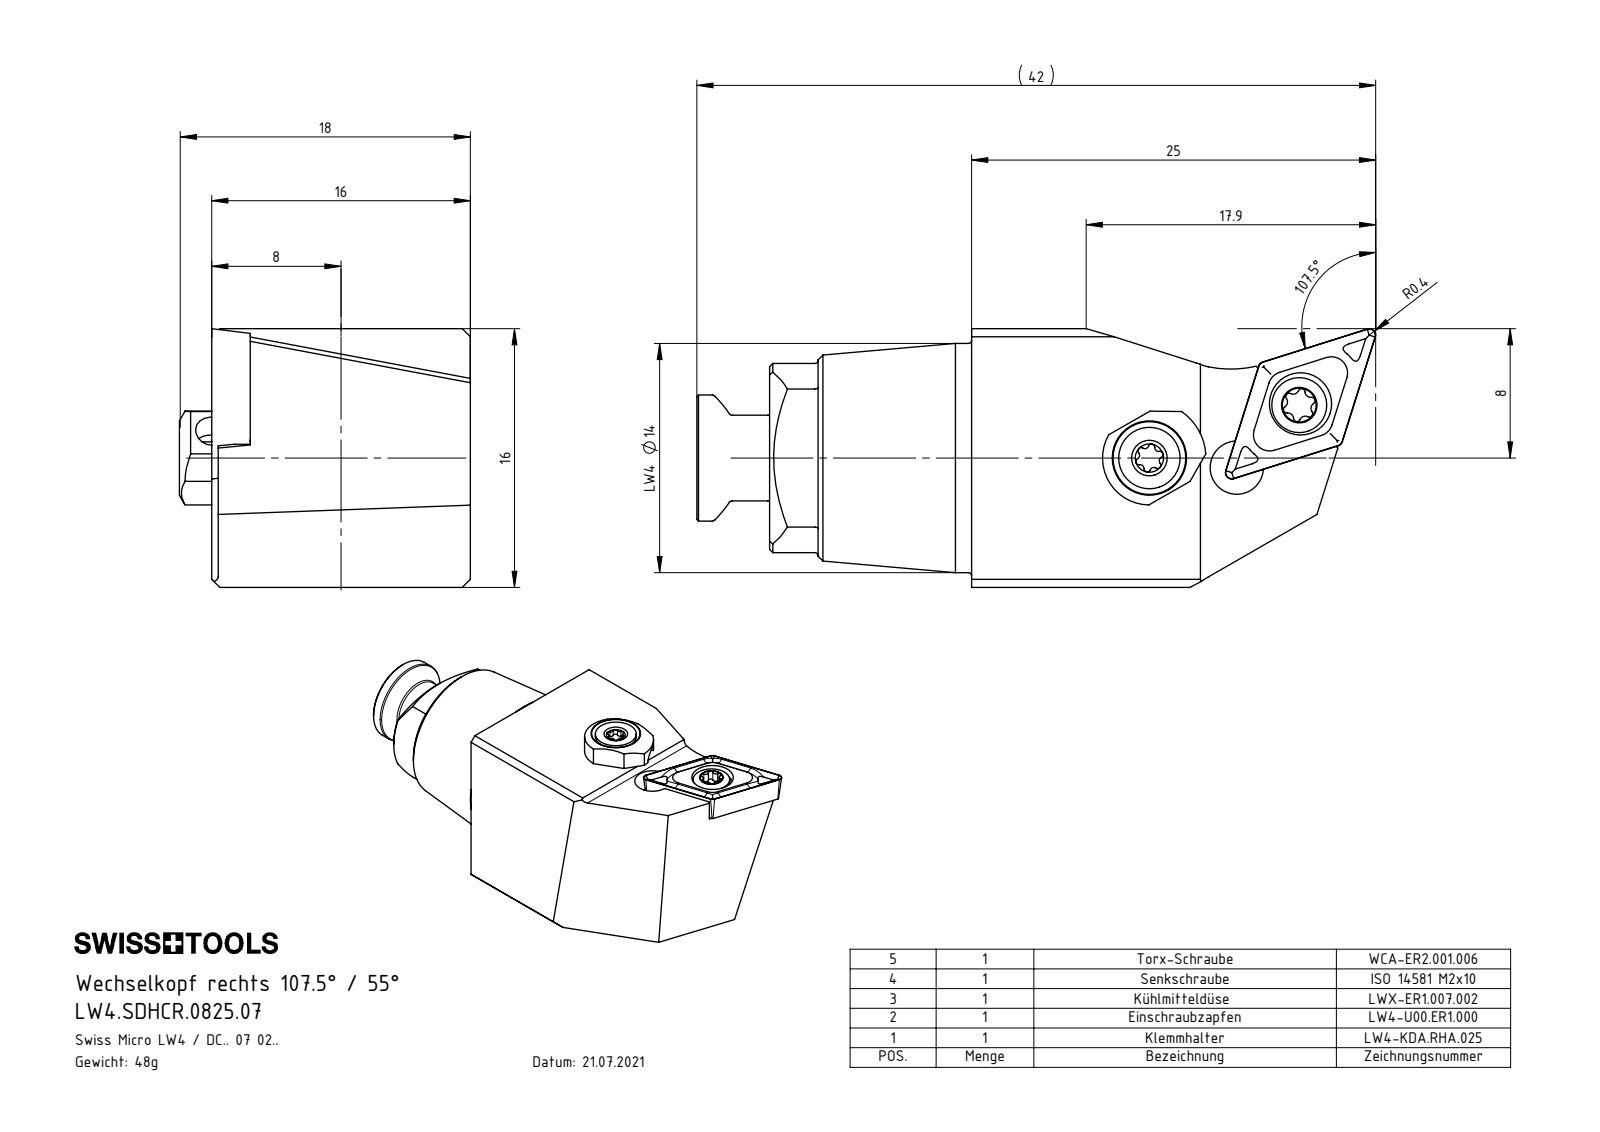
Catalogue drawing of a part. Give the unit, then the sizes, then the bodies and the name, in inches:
Units: inches
Overall size (bounding box): 1.654 × 0.709 × 0.63
Round holes (diameter × count): ⌀0.118 ×2, ⌀0.063 ×1, ⌀0.079 ×1, ⌀0.081 ×1, ⌀0.098 ×1, ⌀0.11 ×1, ⌀0.13 ×1, ⌀0.152 ×1, ⌀0.217 ×1
Round bosses / shafts (diameter × count): ⌀0.558 ×1, ⌀0.303 ×1, ⌀0.236 ×1, ⌀0.209 ×1, ⌀0.197 ×1, ⌀0.15 ×1, ⌀0.134 ×1, ⌀0.098 ×1
Partial cylindrical surfaces — rounded edges, fillets, slot ends (radius × count): R0.008 ×8, R0.008 ×6, R0.009 ×6, R0.014 ×4, R0.014 ×2, R0.02 ×1, R0.039 ×1, R0.114 ×1
Main face-to-face distances: 0.63, 0.536, 0.094, 0.295, 0.614, 0.078, 0.016, 0.079, 0.492, 0.157
Hole centre spacings: 0.214, 0.215, 0.219, 0.387, 0.391
Volume: 0.377 in³ · Surface area: 5.357 in²
Bodies: 6 solids, 259 faces (70 planar, 81 cylindrical, 108 other)
Part name (STEP PRODUCT): LW4-U00.ER1.000_B; WCA-ER2.001.006_A; LW4-KDA.RHA.025_A; LW4.SDHCR.0825.07 (+3 more)
STEP written by: SolidWorks 2022 (CONFIG_CONTROL_DESIGN)
